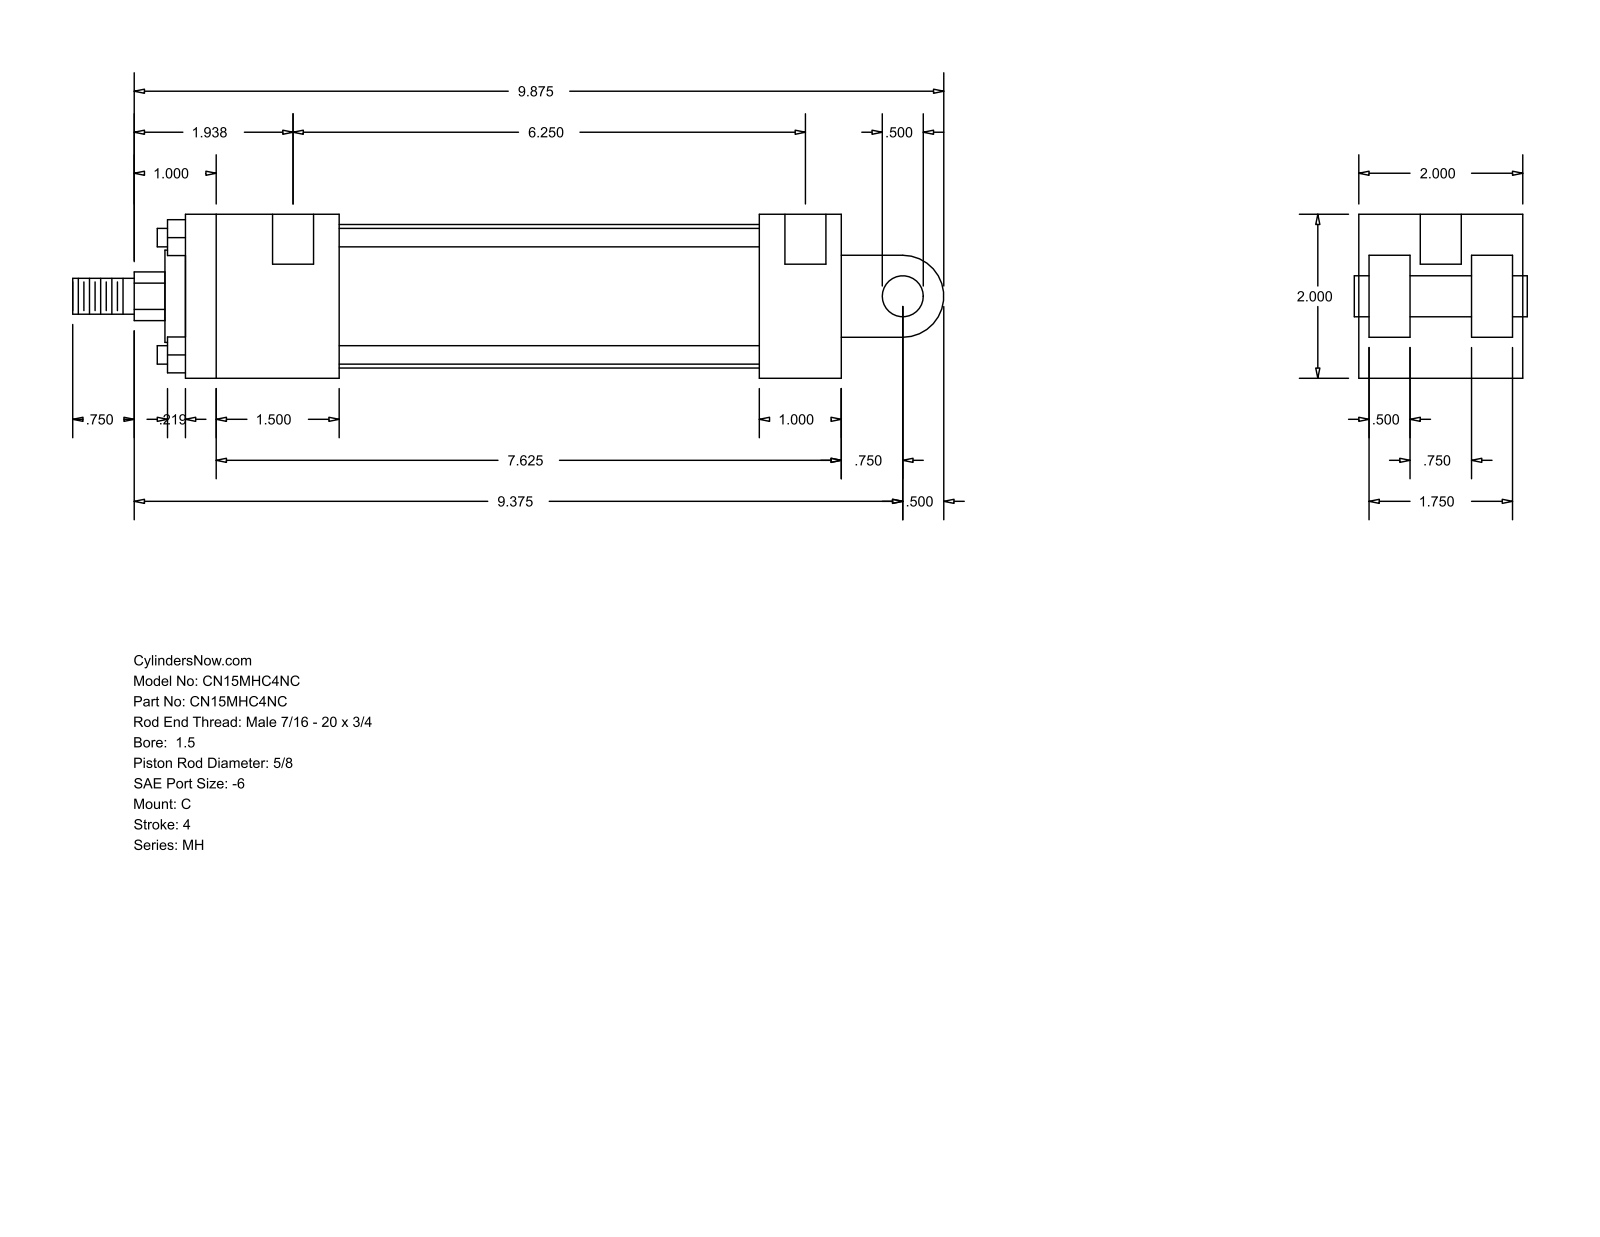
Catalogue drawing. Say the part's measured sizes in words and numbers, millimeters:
The part is named "MH_C__0150_0.625". Its 3-D file was written by "GSSL Pune (CONFIG_CONTROL_DESIGN)". It is 0 solids with 99 faces: 70 planar, 29 cylindrical and 0 other. Overall it measures 269.88 by 50.8 by 50.8 millimeters. Round holes: 4 of diameter 5.56, 2 of diameter 12.7. Round bosses or shafts: 4 of diameter 5.71, 1 of diameter 44.45, 1 of diameter 28.57, 1 of diameter 15.88, 1 of diameter 12.7, 1 of diameter 11.11. Partial cylindrical surfaces (rounded edges, fillets, slot ends): 1 of radius 7.54, 1 of radius 12.7. The main face-to-face distances are 50.8, 12.7, 203.19, 34.93, 3.17, 47.63, 15.87, 31.76, 38.1, 47.62. The hole center spacings are 161.92, 3.17, 158.75.
